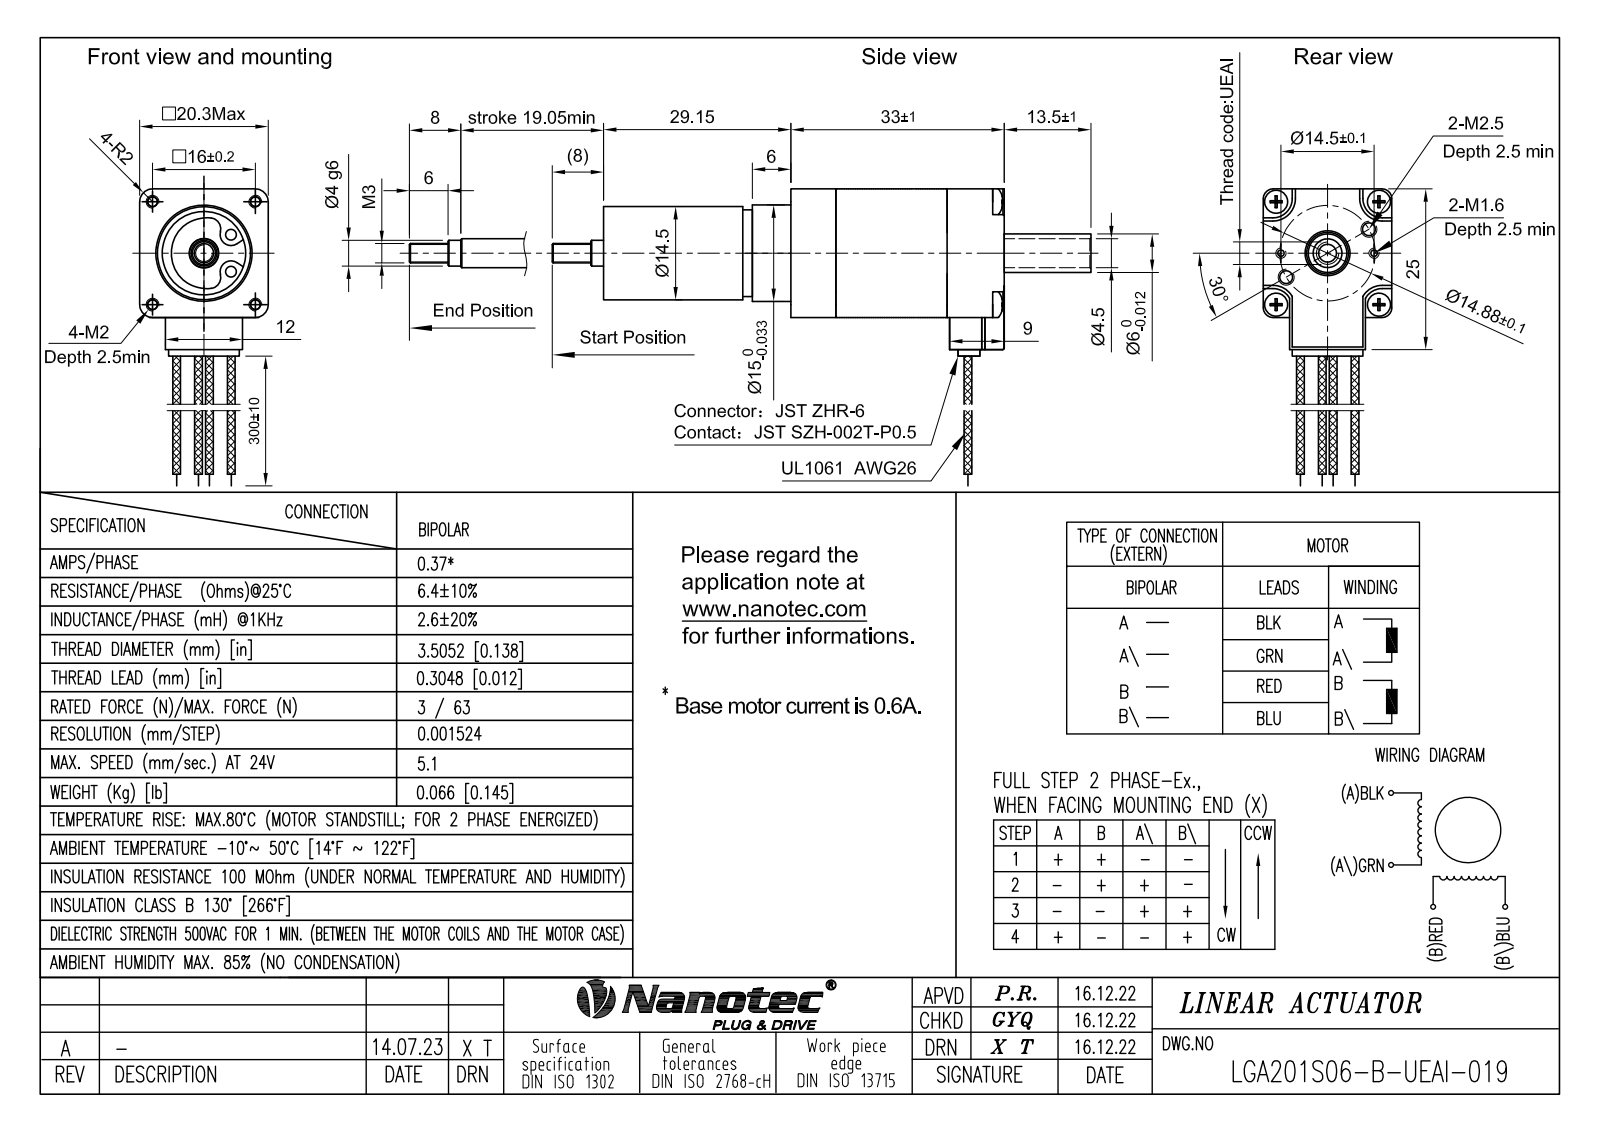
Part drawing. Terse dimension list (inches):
name: 零件1
written by: Autodesk Inventor 2013 (CONFIG_CONTROL_DESIGN)
unit: in
bodies: 1 solid, 302 faces (157 planar, 63 cylindrical, 82 other)
size: 3.843 × 0.984 × 0.787
volume: 1.113 in³; area: 10.89 in²
holes: 6× ⌀0.024, 4× ⌀0.063, 2× ⌀0.048, 2× ⌀0.067, 1× ⌀0.177, 1× ⌀0.256, 1× ⌀0.512
bosses: 12× ⌀0.02, 1× ⌀0.591, 1× ⌀0.571, 1× ⌀0.531, 1× ⌀0.236, 1× ⌀0.157, 1× ⌀0.138, 1× ⌀0.118
rounds: 4× R0.067, 4× R0.079, 1× R0.218, 1× R0.268
face distances: 0.787, 1.307, 1.065, 0.197, 0.984, 2.372, 0.63, 0.354, 0.138, 1.169
hole spacings: 0.059, 0.118, 0.317, 0.445, 0.63, 0.678, 0.177, 0.419
